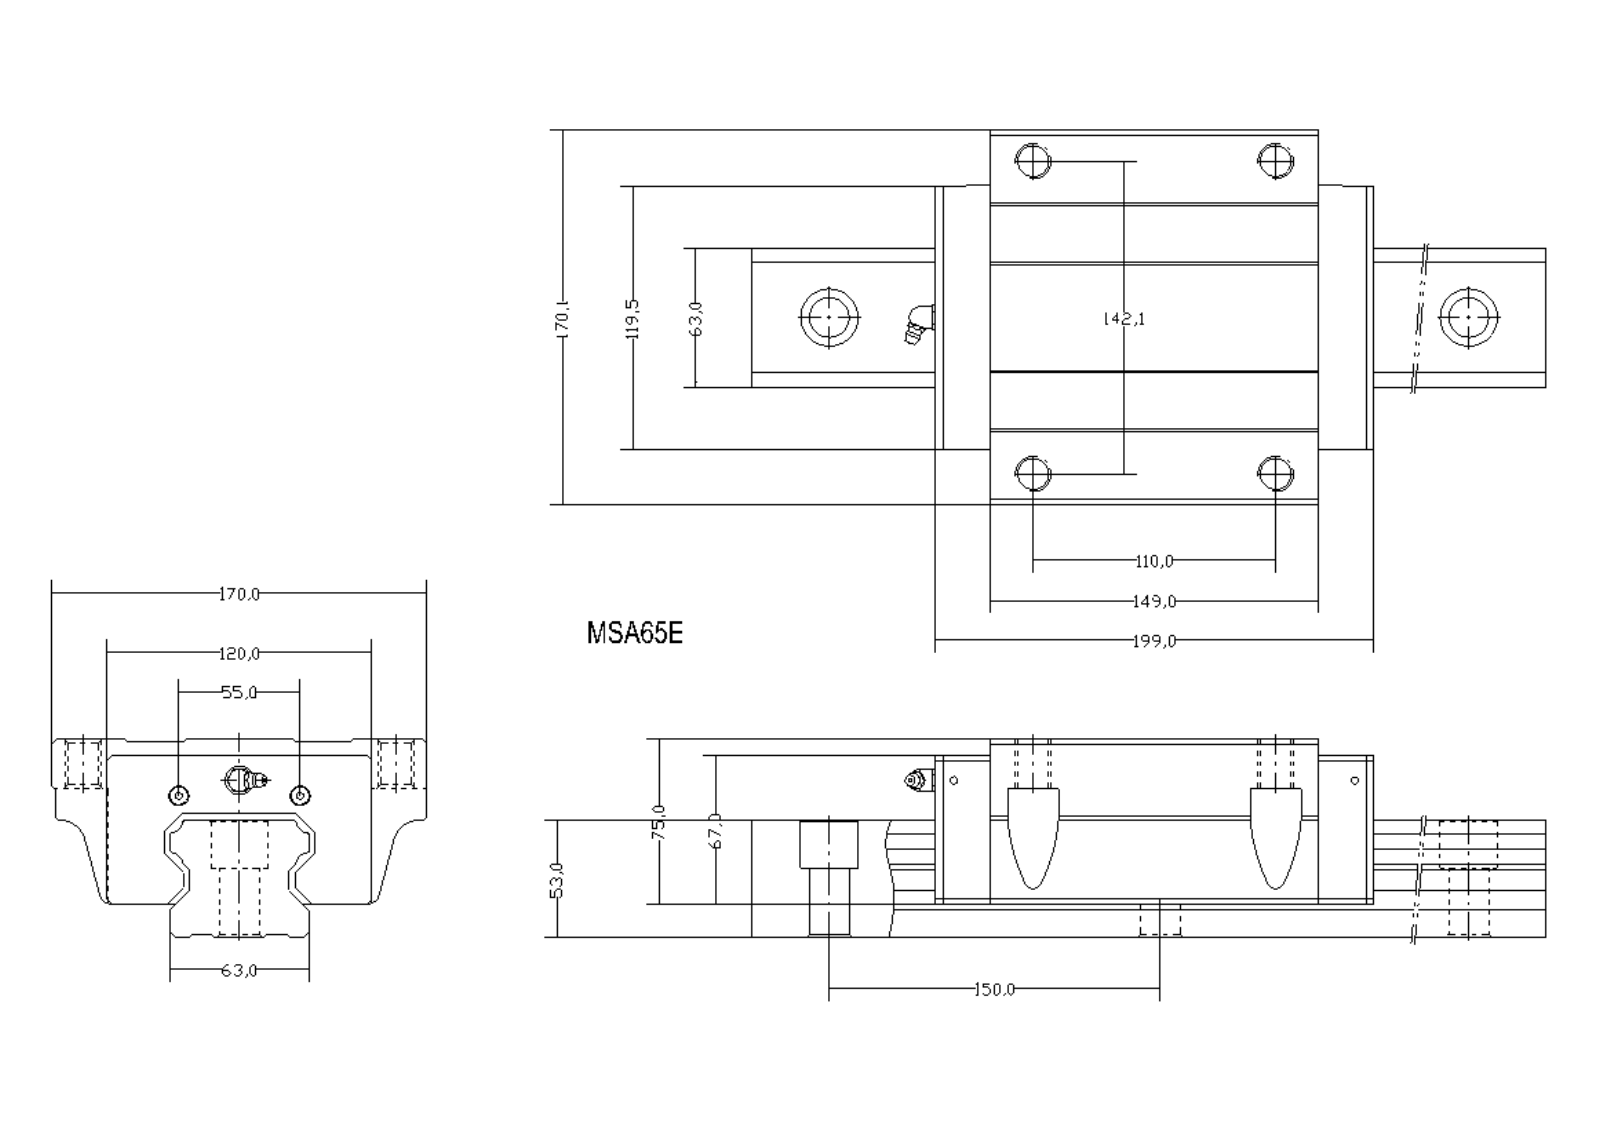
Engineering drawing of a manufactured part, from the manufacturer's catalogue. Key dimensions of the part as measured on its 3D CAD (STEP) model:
STEP written by: Kubotek KeyCreator V6.5.2 (0407) (CONFIG_CONTROL_DESIGN)
Units: millimetres
Bodies: 3 solids, 268 faces (151 planar, 100 cylindrical, 17 other)
Overall size (bounding box): 520 × 170 × 90
Volume: 3 060 000 mm³ · Surface area: 276 844 mm²
Round holes (diameter × count): ⌀16 ×4, ⌀18 ×4, ⌀26 ×4, ⌀3.3 ×2, ⌀4.5 ×2, ⌀9 ×2, ⌀13 ×1
Round bosses / shafts (diameter × count): ⌀10 ×1
Partial cylindrical surfaces — rounded edges, fillets, slot ends (radius × count): R1.3 ×6, R6.3 ×4, R11.5 ×4, R2 ×2, R5 ×2, R6.4 ×2, R12 ×2
Main face-to-face distances: 53, 90, 37, 15, 9.1, 53.9, 25, 75, 38, 52
Hole centre spacings: 150, 28.38, 110, 142, 179.62, 300, 55, 71.6
